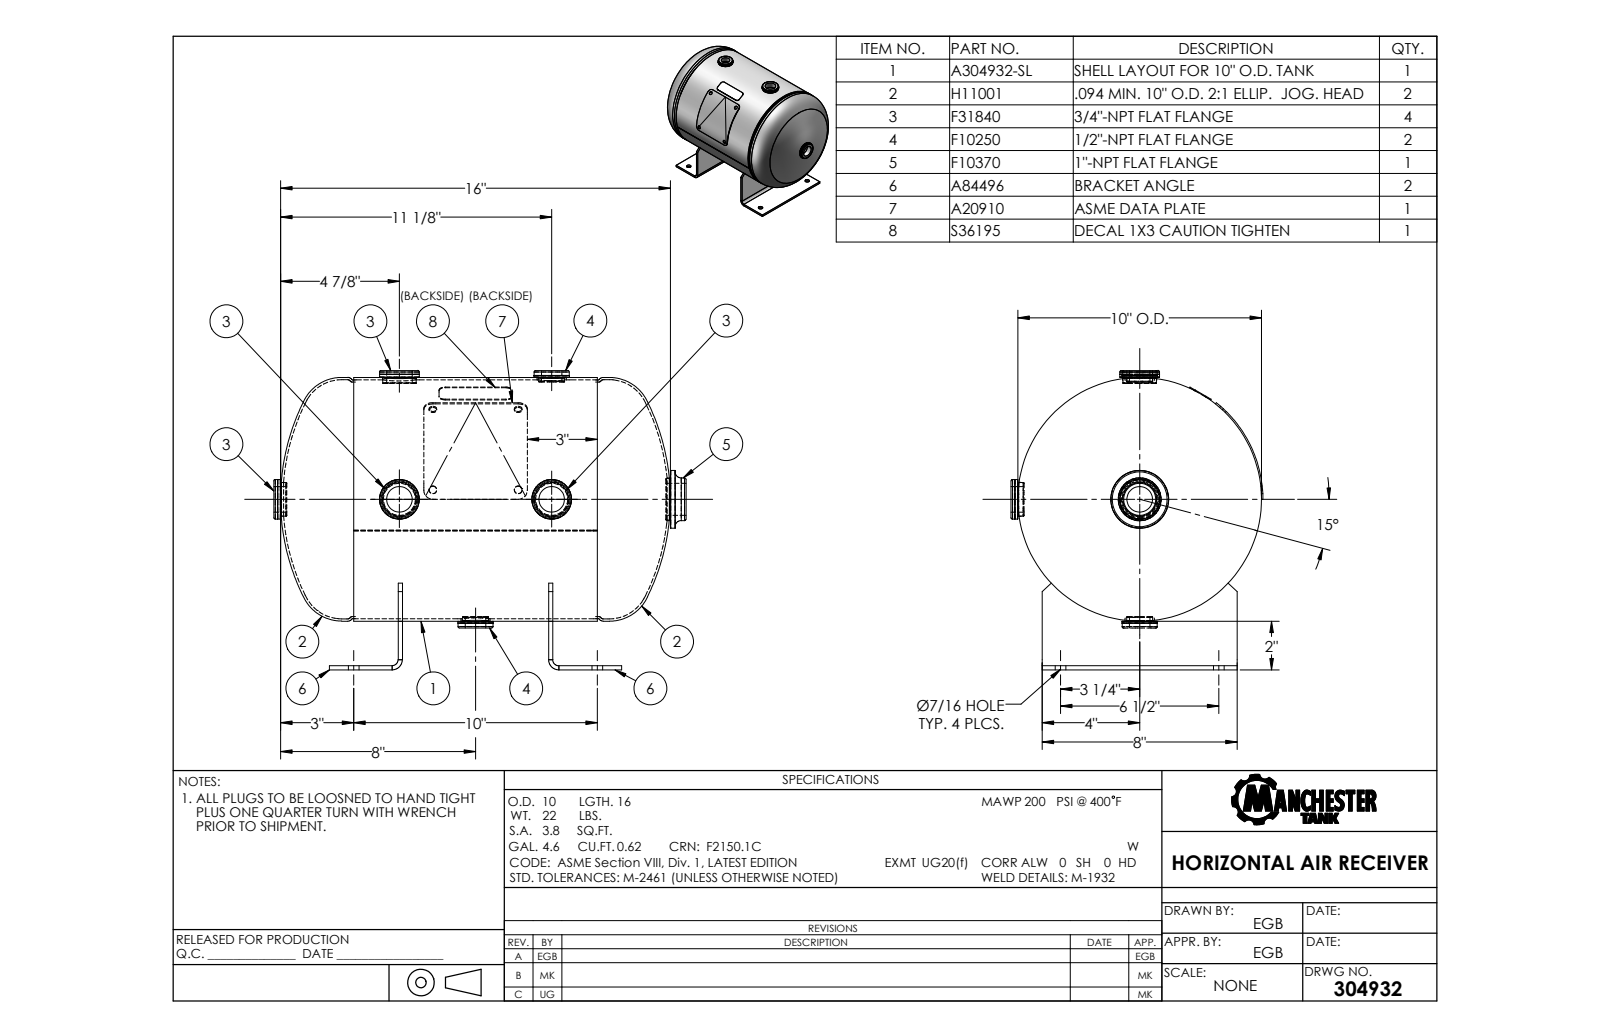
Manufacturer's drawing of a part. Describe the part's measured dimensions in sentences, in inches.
The part is named "304932". Its 3-D file was written by "SolidWorks 2012 (CONFIG_CONTROL_DESIGN)". It is 0 solids with 260 faces: 118 planar, 70 cylindrical and 72 other. Overall it measures 18.173 by 12.844 by 10.904 inches. Round holes: 4 of diameter 0.437. Round bosses or shafts: 4 of diameter 1.63, 4 of diameter 1.05, 3 of diameter 1.625, 2 of diameter 1.45, 2 of diameter 1.438, 2 of diameter 0.84, 1 of diameter 10, 1 of diameter 9.79. Partial cylindrical surfaces (rounded edges, fillets, slot ends): 6 of radius 0.25, 2 of radius 0.429, 1 of radius 5.06. The main face-to-face distances are 0.179, 6.179, 6.358, 6, 8, 1.821, 2, 8.179, 10, 1. The hole center spacings are 6.5, 10, 11.927.
